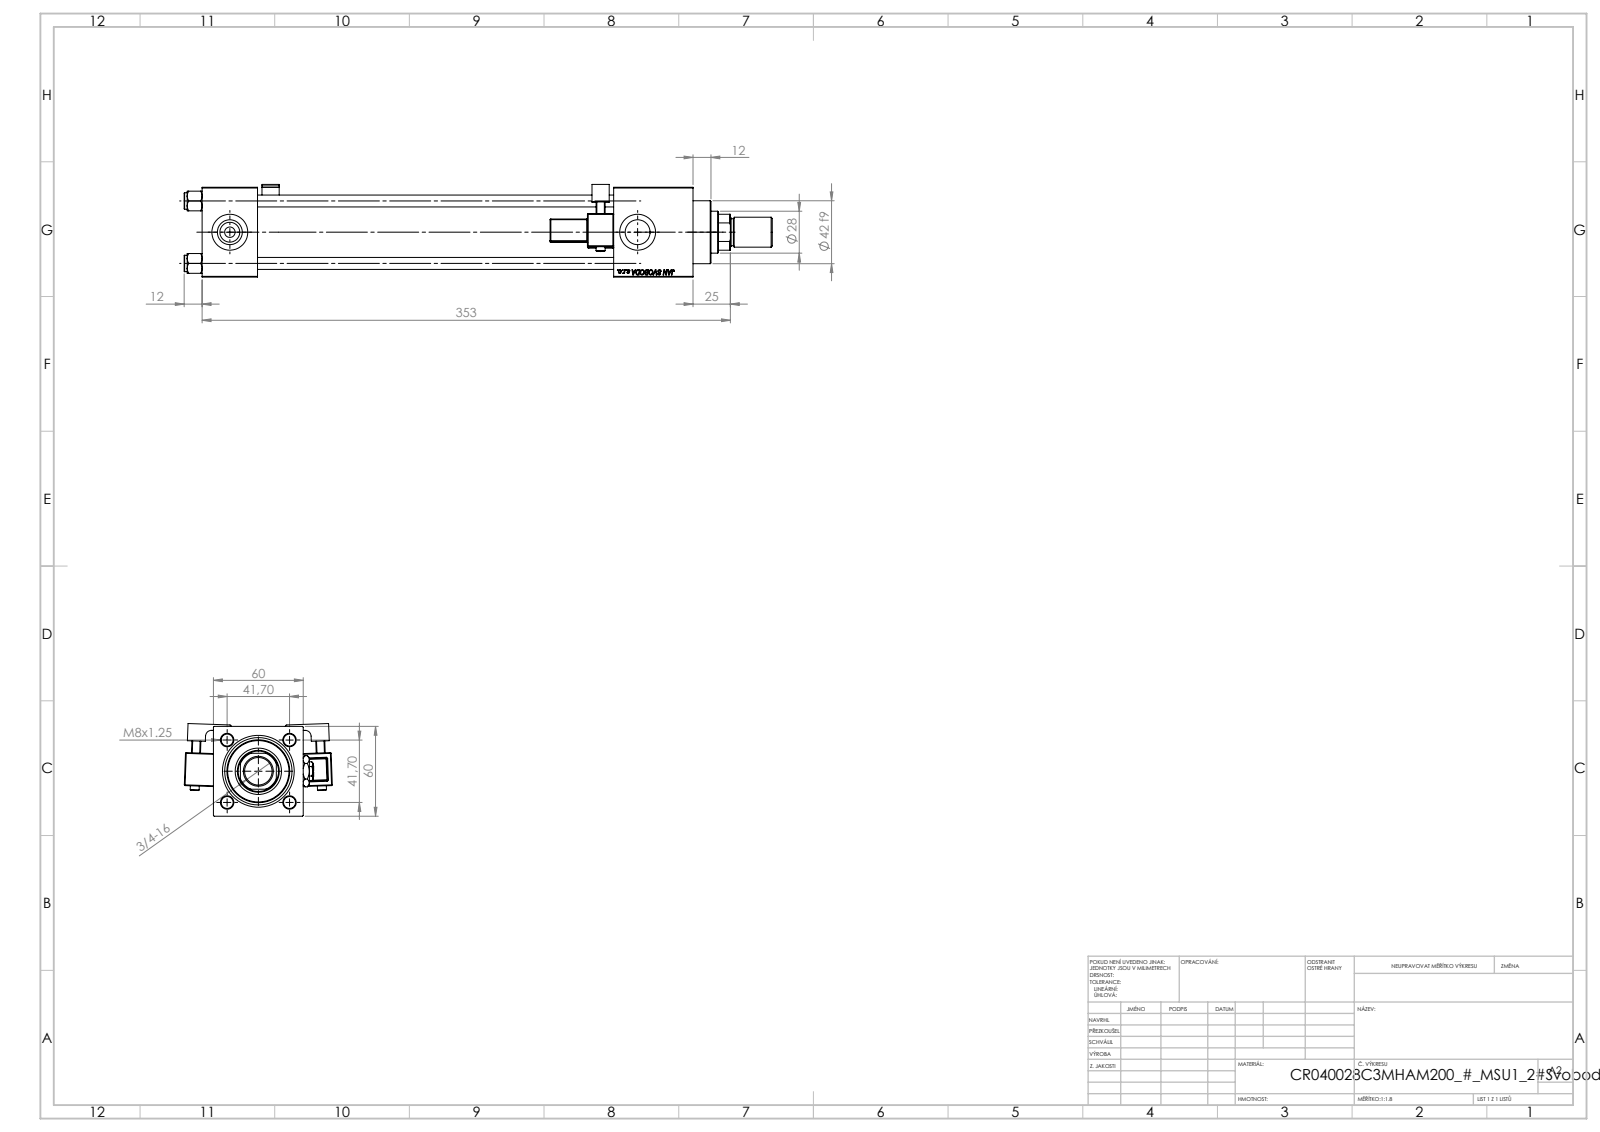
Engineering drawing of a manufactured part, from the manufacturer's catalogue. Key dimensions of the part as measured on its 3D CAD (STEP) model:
Part name (STEP PRODUCT): V215_VC_A; Zatka_pro_OIL_PORT; V215CR_C_Body; ROD_END_AH (+4 more)
STEP written by: SolidWorks 2019 (CONFIG_CONTROL_DESIGN)
Units: millimetres
Bodies: 16 solids, 1418 faces (636 planar, 162 cylindrical, 620 other)
Overall size (bounding box): 393 × 98.85 × 61.9
Volume: 690 401 mm³ · Surface area: 211 432 mm²
Round holes (diameter × count): ⌀8 ×4, ⌀7 ×2, ⌀16.66 ×2, ⌀24 ×2, ⌀18.5 ×1, ⌀28 ×1, ⌀31 ×1, ⌀40 ×1, ⌀45 ×1
Round bosses / shafts (diameter × count): ⌀11 ×4, ⌀6 ×2, ⌀46 ×1, ⌀42 ×1, ⌀20 ×1, ⌀18 ×1
Partial cylindrical surfaces — rounded edges, fillets, slot ends (radius × count): R0.5 ×48, R1 ×2, R2.5 ×2, R4 ×2, R13.5 ×1
Main face-to-face distances: 60, 37, 275, 238, 53, 299.3, 262.3, 24.3, 328, 291
Hole centre spacings: 29.49, 41.7, 58.97, 272.5
